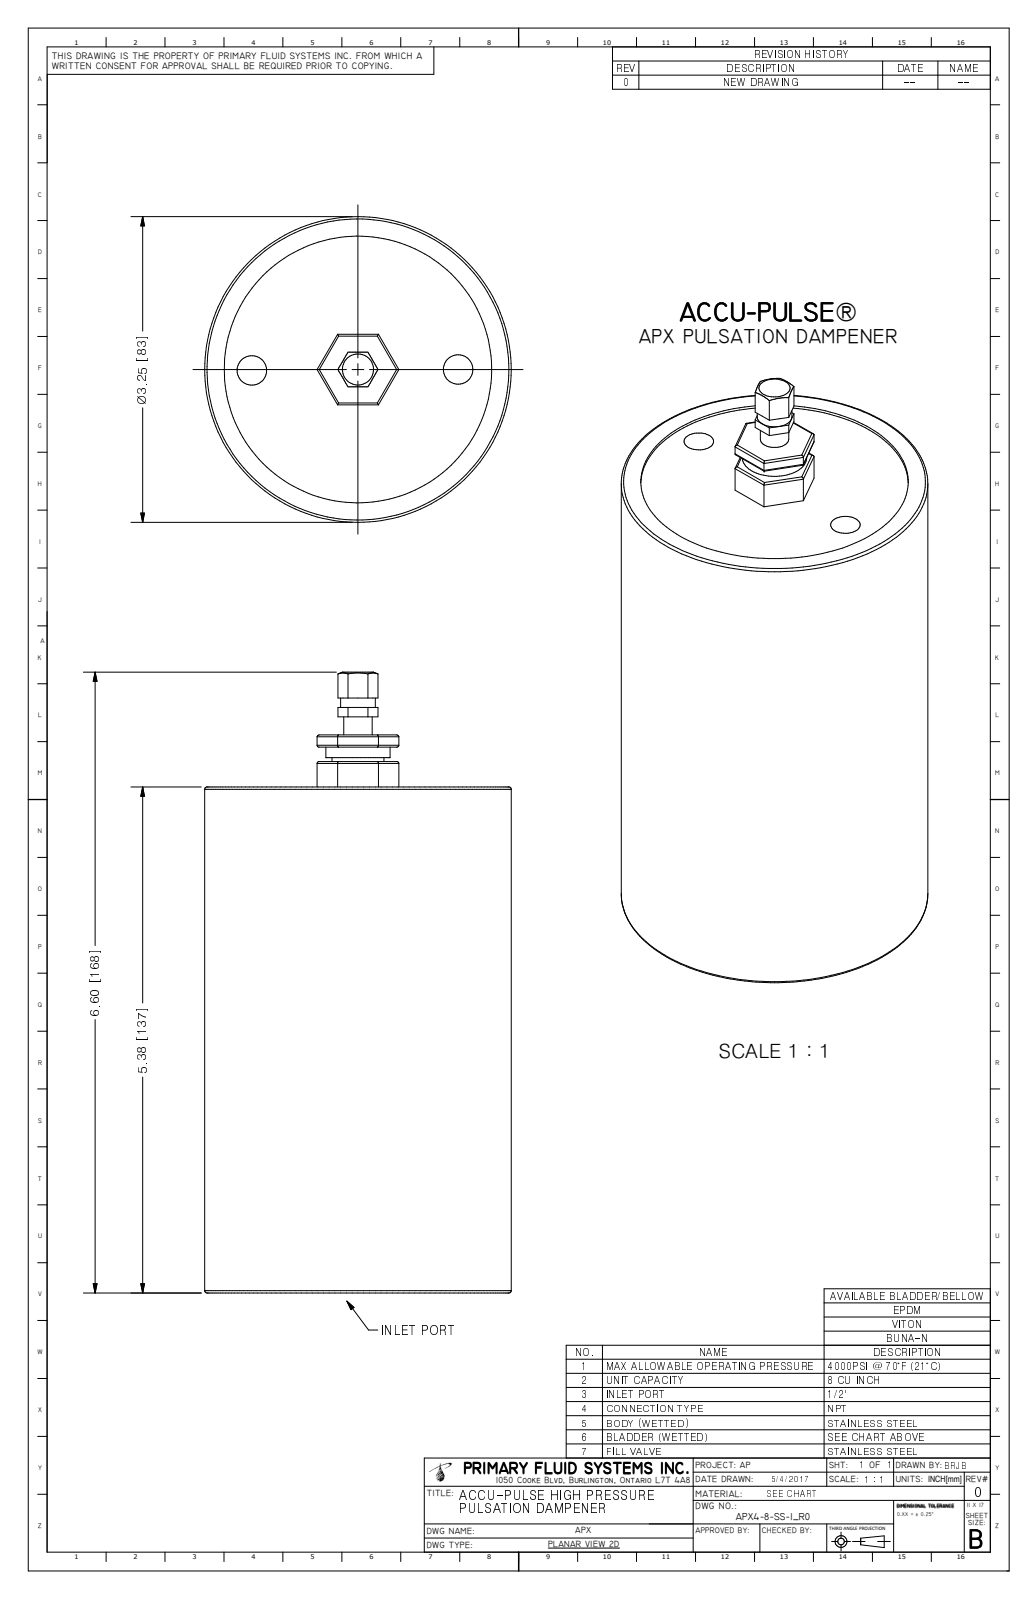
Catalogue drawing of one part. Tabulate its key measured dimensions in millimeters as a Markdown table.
| quantity | value |
| --- | --- |
| part name | APX4-8-SS-1_R0 |
| STEP written by | Autodesk Inventor 2009 (AUTOMOTIVE_DESIGN) |
| units | millimeters |
| bodies | 2 solids, 81 faces (50 planar, 28 cylindrical, 3 other) |
| overall size | 167.6 × 82.6 × 82.6 |
| volume | 729 100 mm³ |
| surface area | 50 060 mm² |
| round holes (diameter × count) | 8 × 2, 21.3 × 1, 72 × 1 |
| round bosses / shafts (diameter × count) | 82.6 × 1, 17.3 × 1, 14 × 1, 9.3 × 1, 7.6 × 1 |
| partial cylindrical surfaces (radius × count) | 0.5 × 18 |
| main face-to-face distances | 135.9, 136.7, 0.8, 9.7, 126.2, 127, 19.1, 14.2, 4.9, 150.7 |
| hole center spacings | 27, 28.6, 55.5 |
